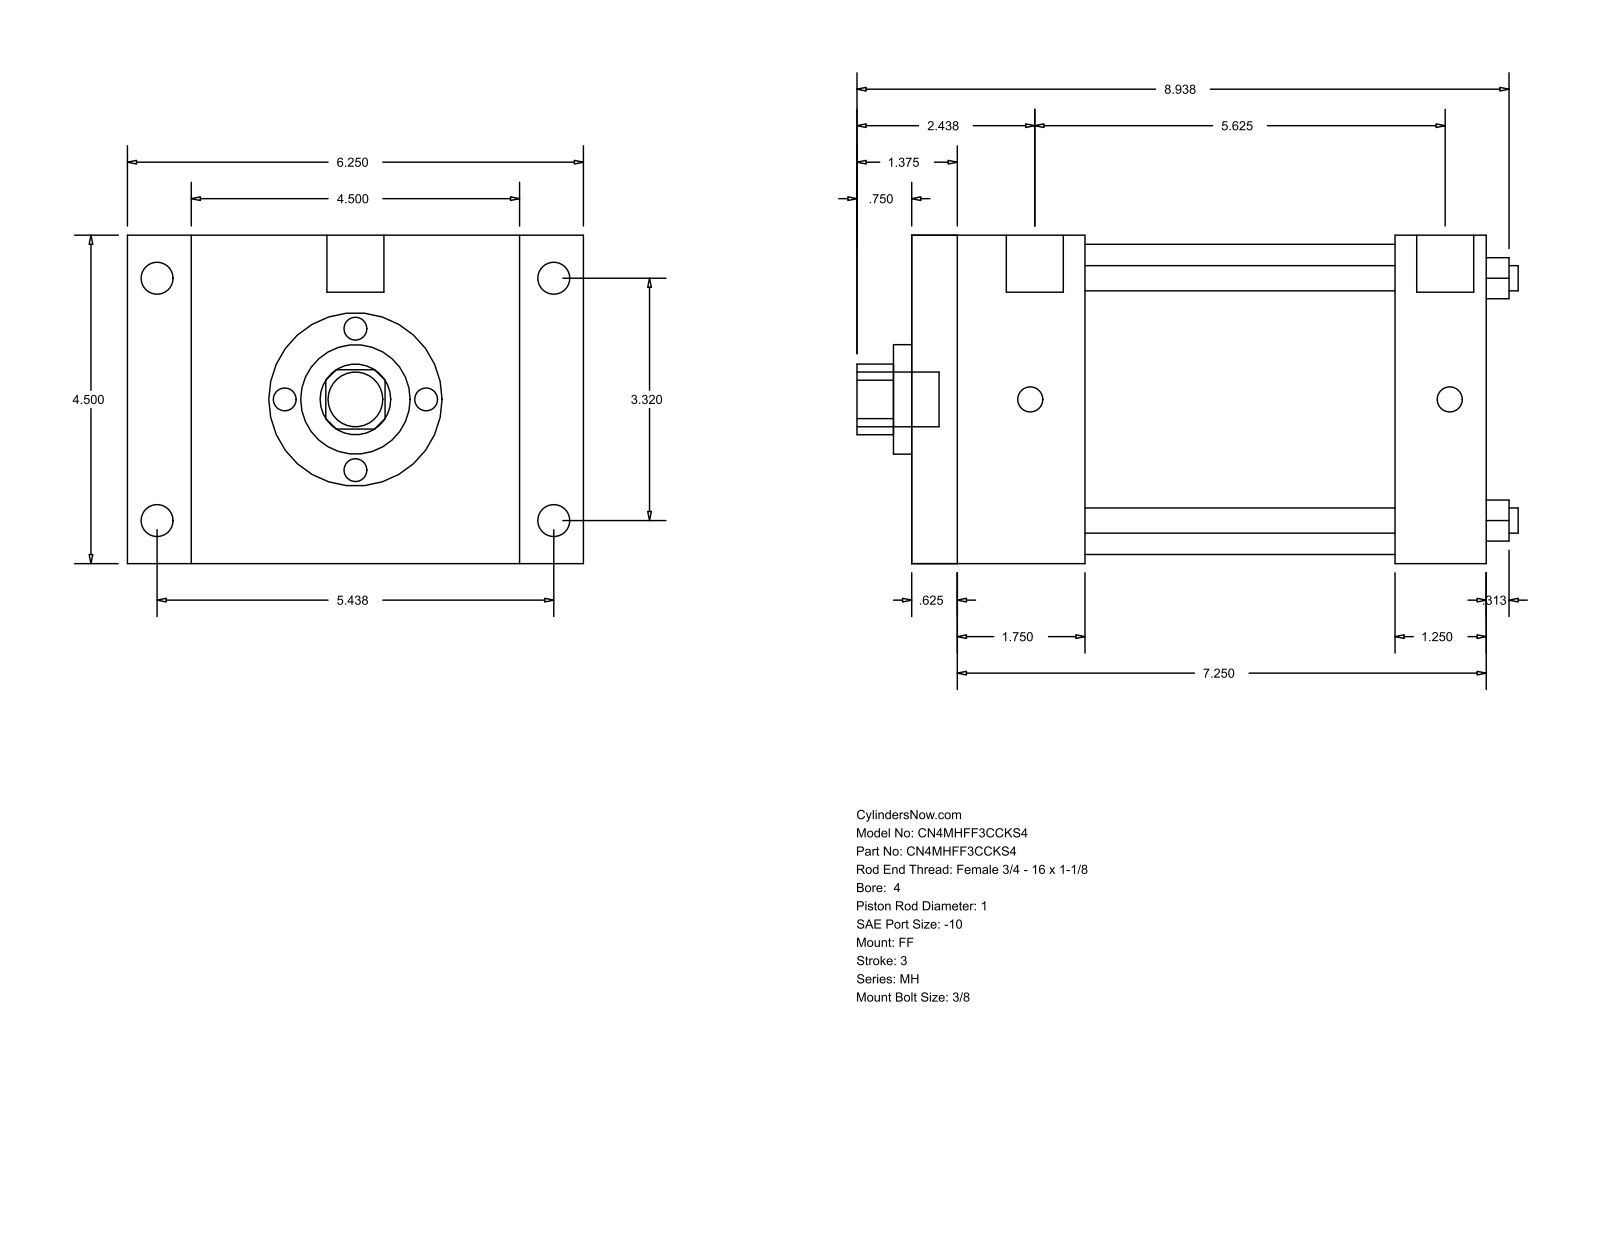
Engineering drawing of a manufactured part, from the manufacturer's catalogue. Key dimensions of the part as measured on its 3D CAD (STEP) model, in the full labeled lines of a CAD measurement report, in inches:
Part name (STEP PRODUCT): MH_FF__0400_1
STEP written by: GSSL Pune (CONFIG_CONTROL_DESIGN)
Units: inches
Bodies: 0 solids, 92 faces (64 planar, 28 cylindrical, 0 other)
Overall size (bounding box): 9.063 × 6.25 × 4.5
Round holes (diameter × count): ⌀0.345 ×4, ⌀1 ×1, ⌀1.5 ×1, ⌀4.25 ×1
Round bosses / shafts (diameter × count): ⌀0.438 ×4, ⌀0.344 ×4, ⌀0.781 ×2, ⌀0.75 ×1
Partial cylindrical surfaces — rounded edges, fillets, slot ends (radius × count): R0.484 ×1
Main face-to-face distances: 4.5, 7.875, 0.625, 7.25, 2.375, 1.75, 5.5, 6.625, 6, 4.25
Hole centre spacings: 2.347, 3.32, 4.695
